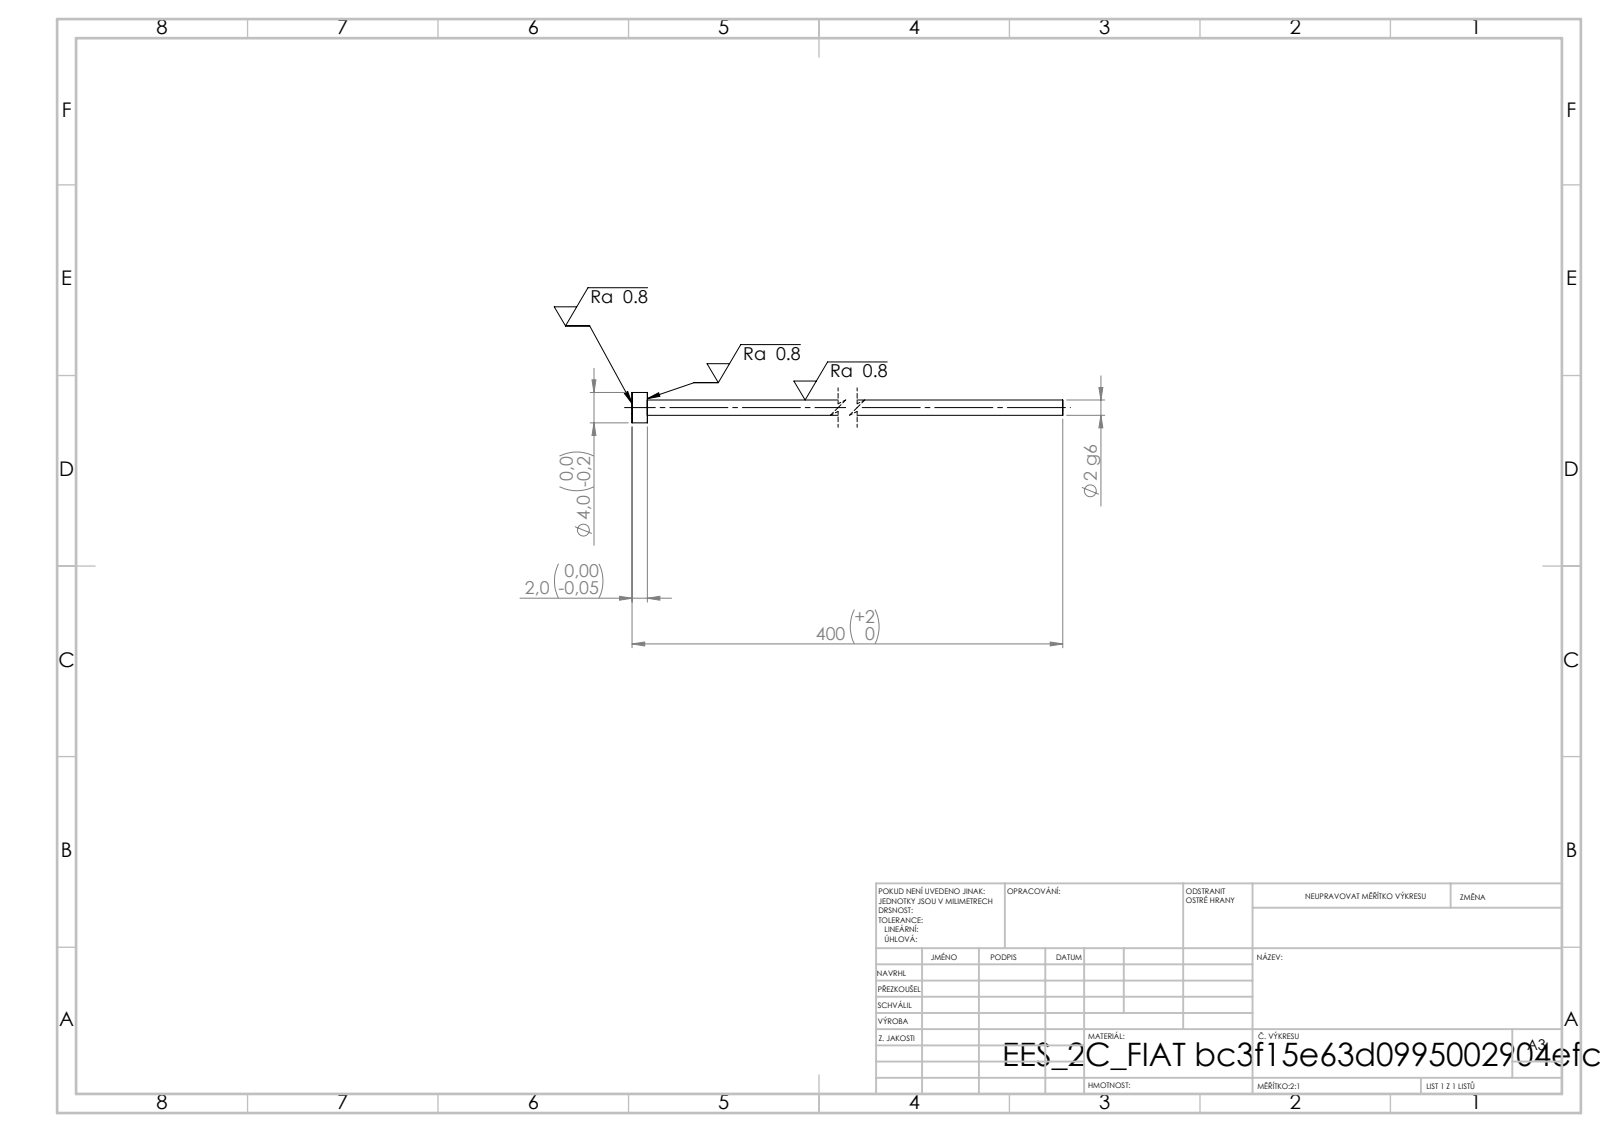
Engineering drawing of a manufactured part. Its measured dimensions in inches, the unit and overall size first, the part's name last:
Units: inches
Overall size (bounding box): 15.748 × 0.157 × 0.157
Round bosses / shafts (diameter × count): ⌀0.157 ×1, ⌀0.079 ×1
Main face-to-face distances: 0.079, 15.748, 15.669
Volume: 0.078 in³ · Surface area: 3.954 in²
Bodies: 1 solid, 7 faces (3 planar, 4 cylindrical, 0 other)
STEP written by: SolidWorks 2019 (CONFIG_CONTROL_DESIGN)
